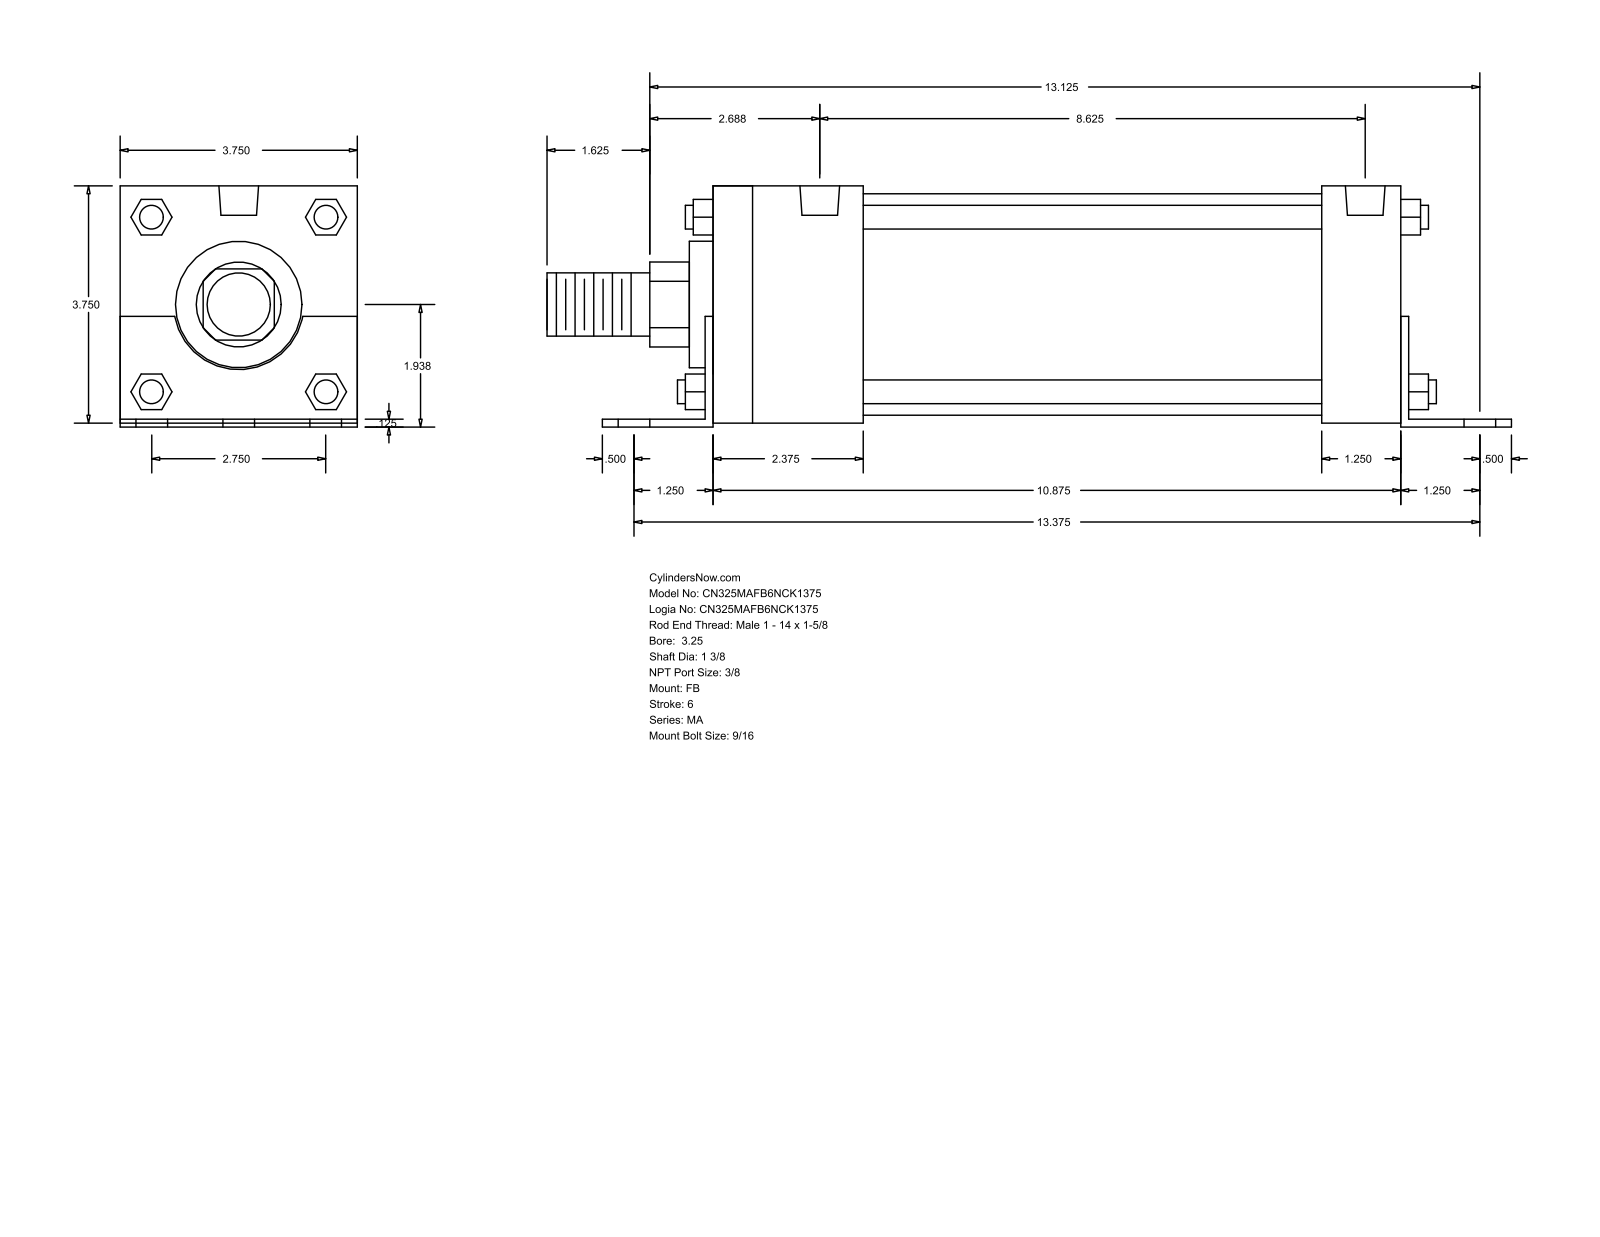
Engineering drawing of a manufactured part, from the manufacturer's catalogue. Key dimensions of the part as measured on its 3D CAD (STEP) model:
Part name (STEP PRODUCT): MA_FB__0325_1.375
STEP written by: GSSL Pune (CONFIG_CONTROL_DESIGN)
Units: millimetres
Bodies: 0 solids, 140 faces (105 planar, 35 cylindrical, 0 other)
Overall size (bounding box): 387.35 × 96.84 × 95.25
Round holes (diameter × count): ⌀14.29 ×6, ⌀11.11 ×4, ⌀15.93 ×2
Round bosses / shafts (diameter × count): ⌀9.53 ×4, ⌀88.9 ×1, ⌀50.8 ×1, ⌀34.92 ×1, ⌀25.4 ×1
Partial cylindrical surfaces — rounded edges, fillets, slot ends (radius × count): R17.06 ×1, R26.16 ×1
Main face-to-face distances: 95.24, 3.17, 1.59, 96.83, 1.58, 93.66, 3.18, 276.22, 279.4, 34.92
Hole centre spacings: 34.92, 341.52, 339.73, 4.77, 57.78, 61.65, 69.84, 82.38
